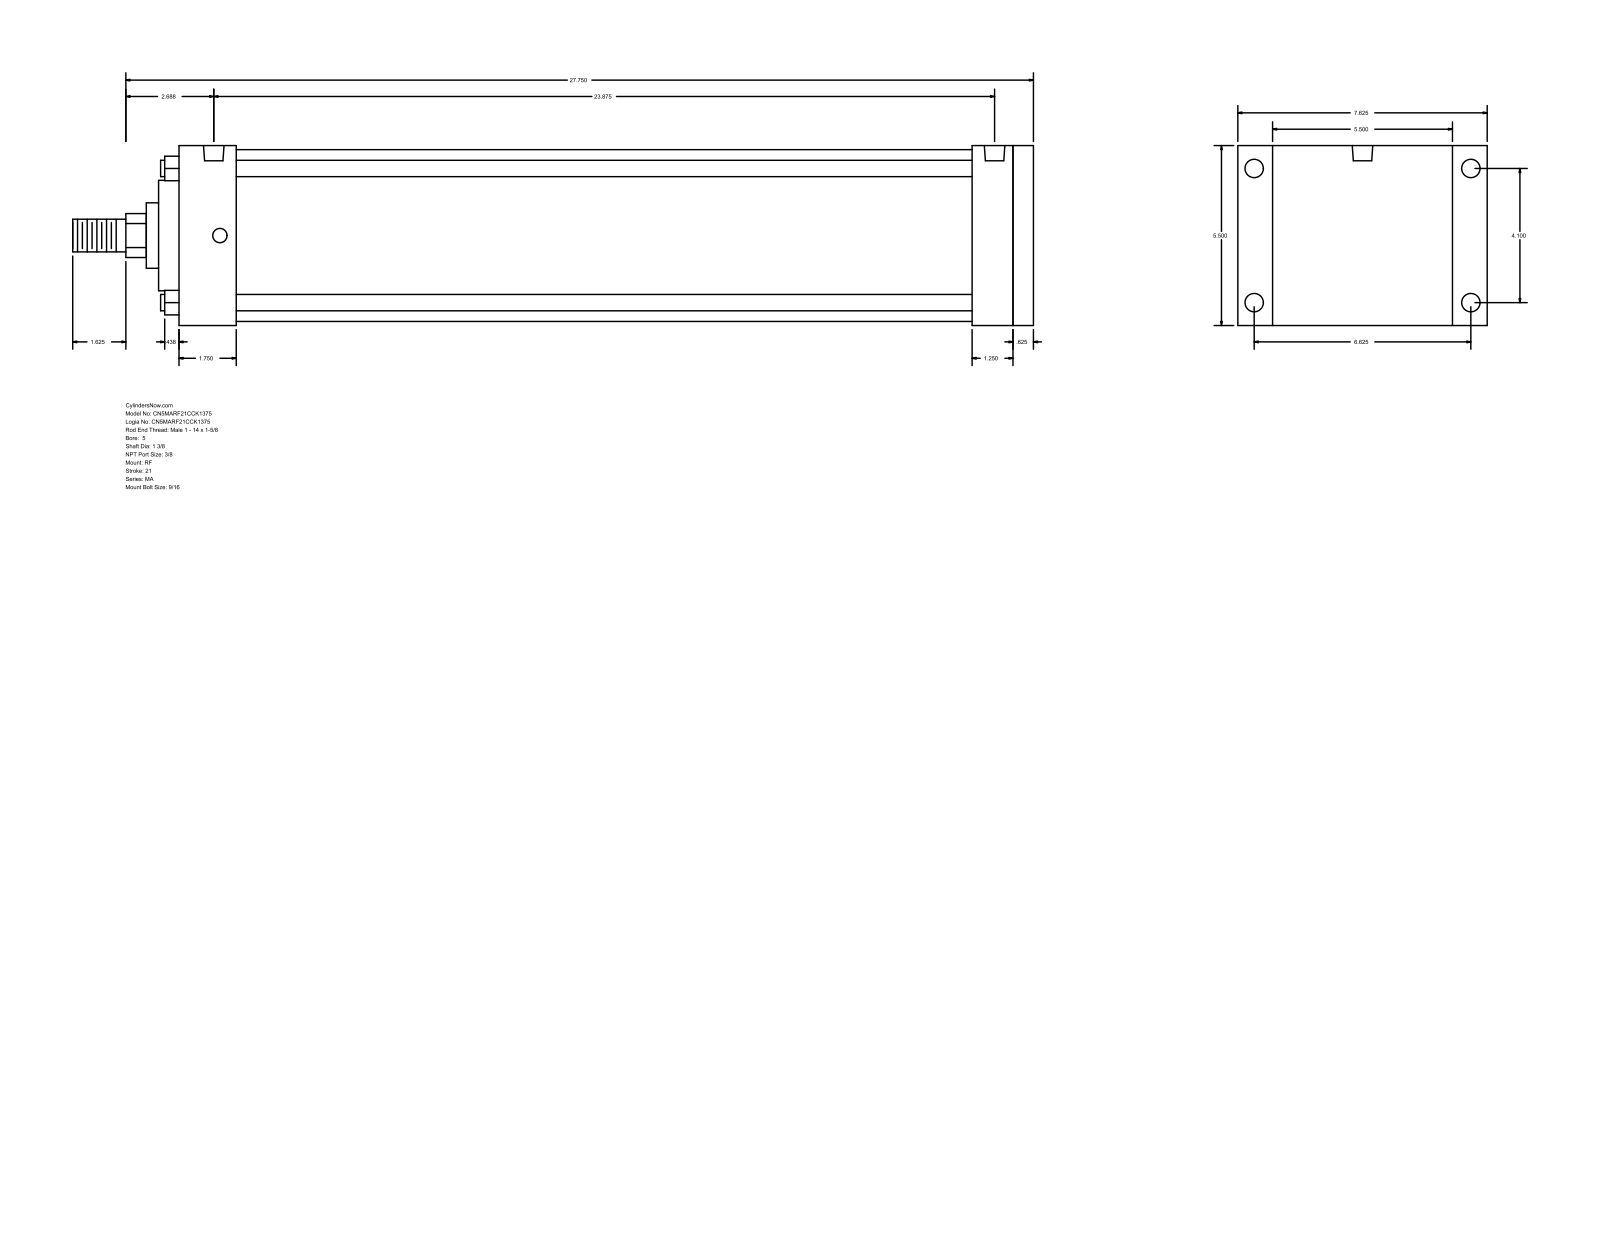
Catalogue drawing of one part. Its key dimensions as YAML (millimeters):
part_name: "MA_RF__0500_1.375"
step_written_by: "GSSL Pune (CONFIG_CONTROL_DESIGN)"
units: millimeters
bodies: {solids: 0, faces: 94, planar: 65, cylindrical: 29, other: 0}
overall_size: [746.12, 193.68, 139.7]
round_holes:
  - {diameter: 11.11, count: 4}
  - {diameter: 14.29, count: 4}
  - {diameter: 15.93, count: 2}
round_bosses_or_shafts:
  - {diameter: 12.7, count: 4}
  - {diameter: 133.35, count: 1}
  - {diameter: 85.72, count: 1}
  - {diameter: 50.8, count: 1}
  - {diameter: 34.92, count: 1}
  - {diameter: 25.4, count: 1}
partial_cylinders:
  - {radius: 17.06, count: 1}
face_to_face_distances: [139.7, 663.58, 15.87, 647.71, 44.45, 603.26, 619.13, 615.96, 571.51, 31.75]
hole_center_spacings: [4.77, 104.14, 168.28, 197.9, 596.89, 601.66, 606.43]
